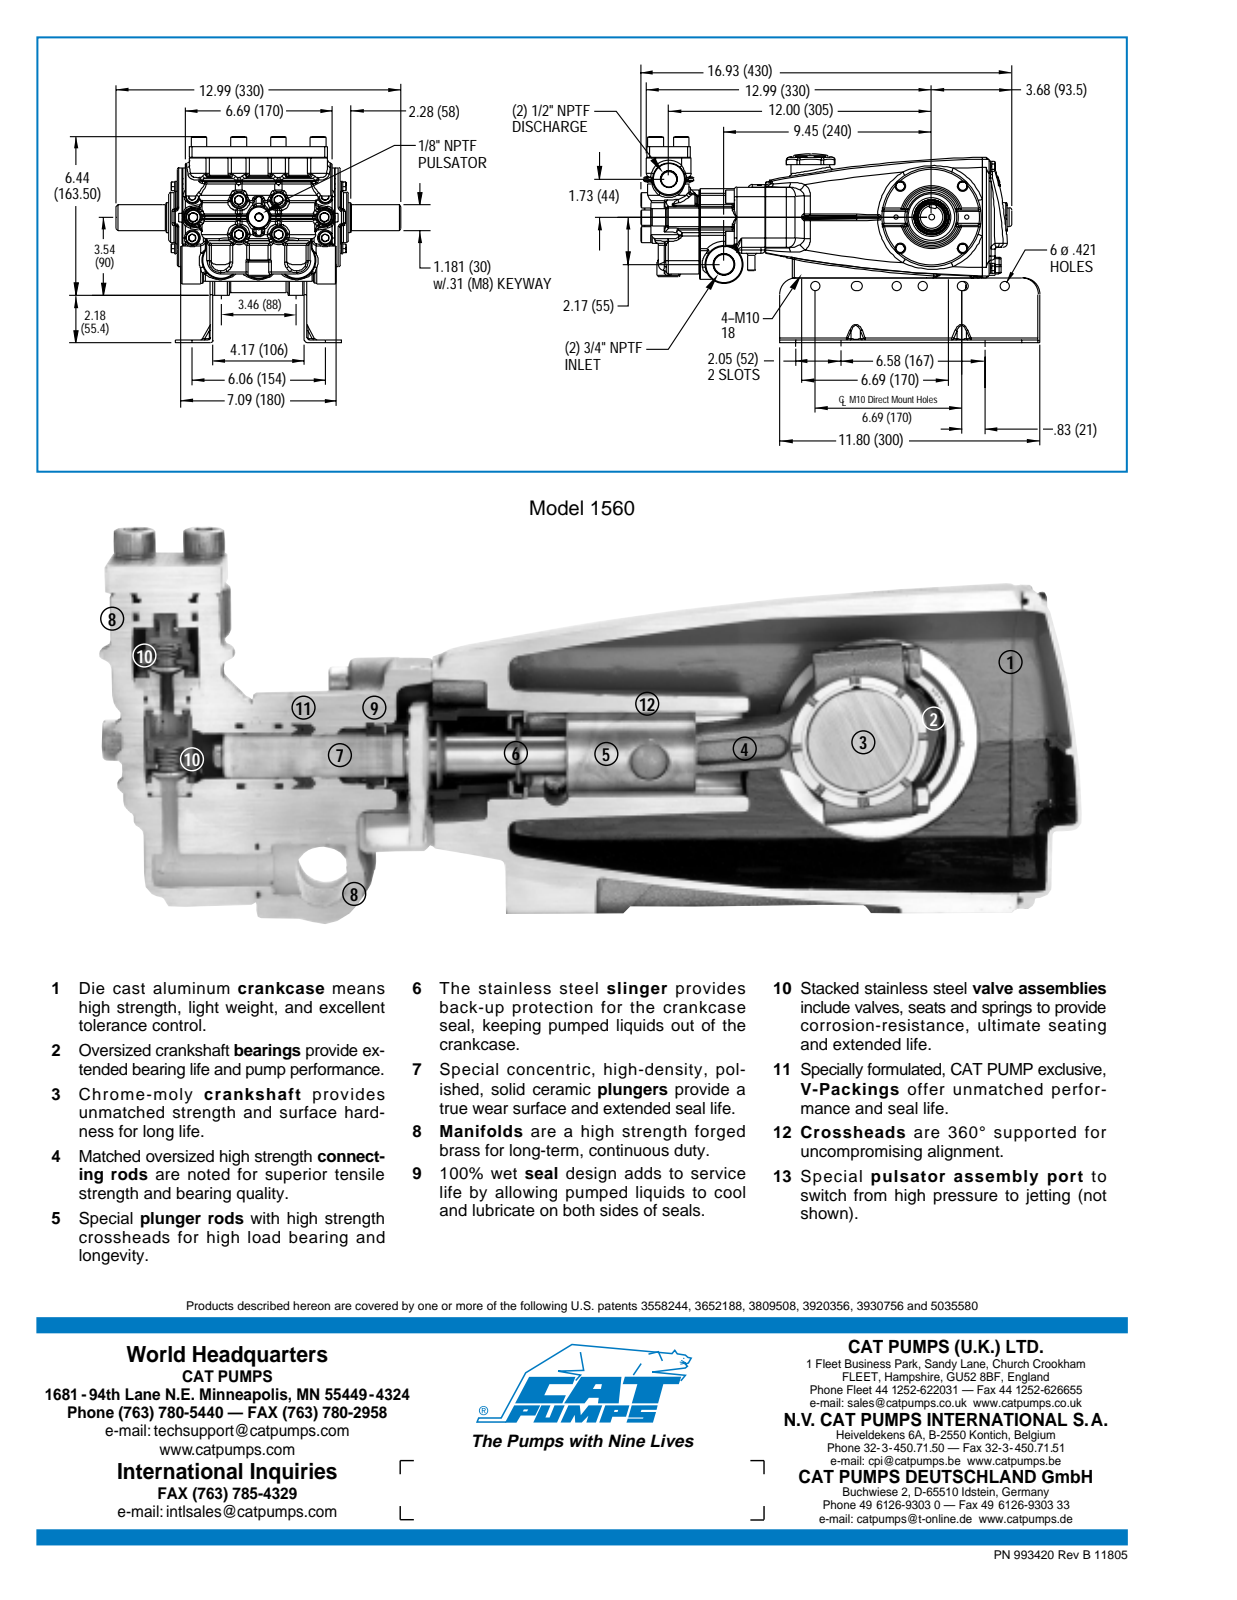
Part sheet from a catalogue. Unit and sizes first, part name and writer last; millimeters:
Units: millimetres
Overall size (bounding box): 429.5 × 330 × 184
Round holes (diameter × count): ⌀10.11 ×14, ⌀13 ×9, ⌀6.1 ×8, ⌀6.4 ×8, ⌀8.38 ×8, ⌀13.5 ×8, ⌀5 ×7, ⌀24 ×7, ⌀4.92 ×6, ⌀6.5 ×6, ⌀11 ×6, ⌀30 ×6
Round bosses / shafts (diameter × count): ⌀12 ×17, ⌀18 ×14, ⌀6 ×10, ⌀12.2 ×8, ⌀20 ×7, ⌀45 ×4, ⌀35 ×4, ⌀16 ×4
Partial cylindrical surfaces — rounded edges, fillets, slot ends (radius × count): R2 ×197, R3 ×80, R5 ×41, R11 ×29, R10 ×16, R4 ×14, R1 ×12, R8 ×12
Main face-to-face distances: 12, 3, 6, 0.35, 176.35, 34, 6.35, 182.35, 182.7, 23
Hole centre spacings: 27.46, 46, 44, 70.61, 88, 36.62, 54.92, 59.36
Volume: 3 830 000 mm³ · Surface area: 1 005 000 mm²
Bodies: 68 solids, 5144 faces (1170 planar, 1467 cylindrical, 2507 other)
Part name (STEP PRODUCT): 1560
STEP written by: SolidWorks 2009 (CONFIG_CONTROL_DESIGN)
